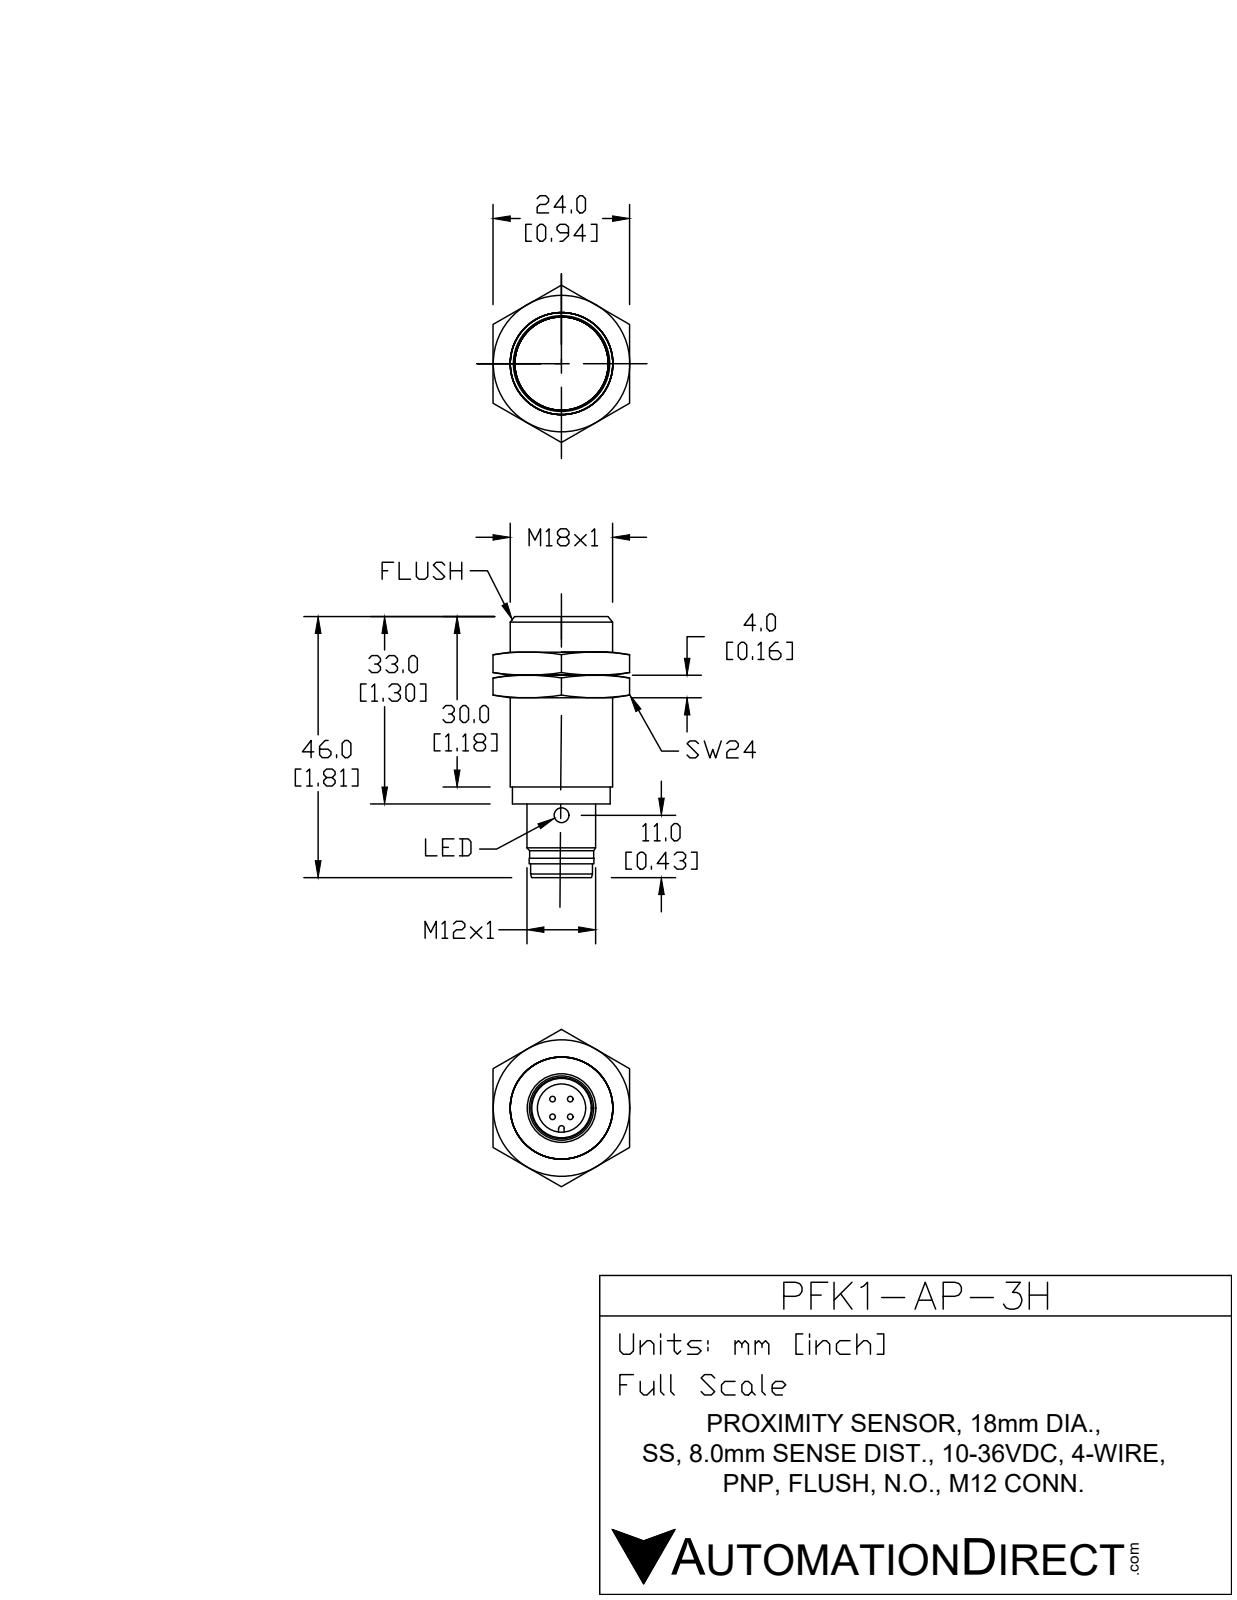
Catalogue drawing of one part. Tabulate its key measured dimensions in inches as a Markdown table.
| quantity | value |
| --- | --- |
| part name | PFK1-AP-3H |
| STEP written by | SolidWorks 2017 (AUTOMOTIVE_DESIGN) |
| units | inches |
| bodies | 3 solids, 112 faces (25 planar, 35 cylindrical, 52 other) |
| overall size | 1.811 × 1.091 × 0.945 |
| volume | 0.681 in³ |
| surface area | 7.866 in² |
| round holes (diameter × count) | 0.098 × 2, 0.331 × 1, 0.666 × 1 |
| round bosses / shafts (diameter × count) | 0.709 × 1, 0.654 × 1, 0.63 × 1, 0.472 × 1, 0.445 × 1, 0.417 × 1 |
| partial cylindrical surfaces (radius × count) | 0.024 × 1, 0.197 × 1 |
| main face-to-face distances | 0.157, 0.945, 0.315, 0.472, 0.787, 0.63, 0.512, 1.299, 0.669, 0.827 |
